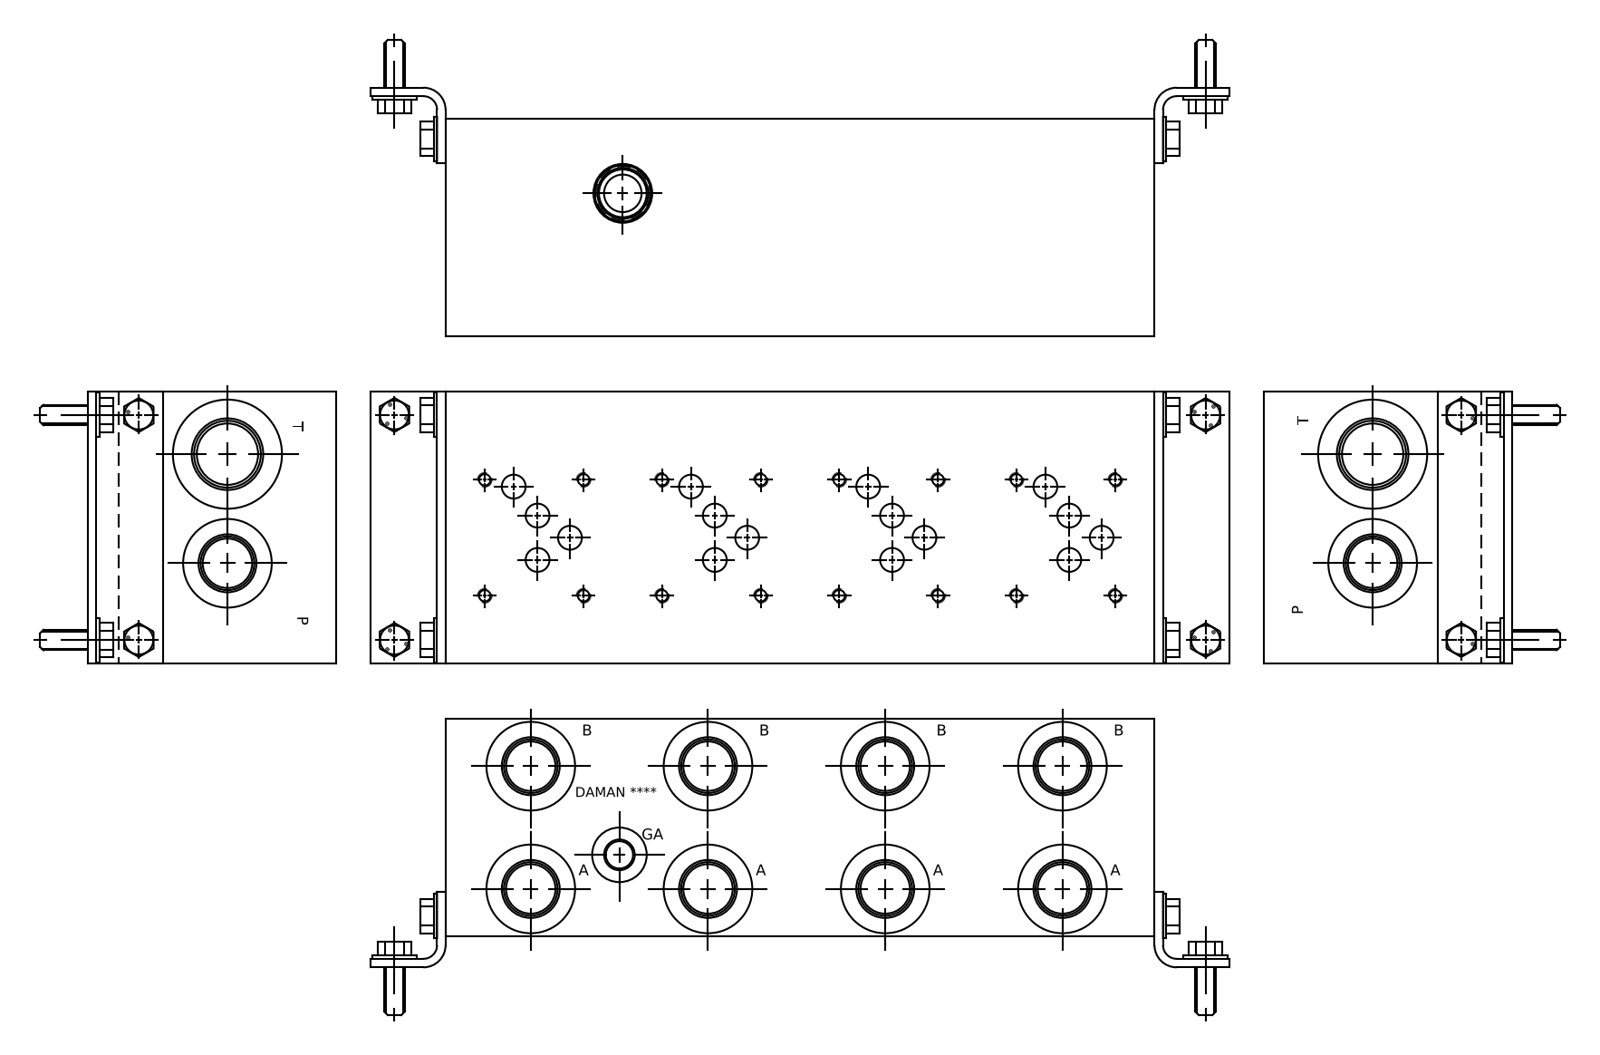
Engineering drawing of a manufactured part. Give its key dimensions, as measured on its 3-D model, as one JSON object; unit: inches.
{"part_name": "Part_DD05HP043S~S_3D", "step_written_by": "Autodesk Inventor 2019 (AUTOMOTIVE_DESIGN)", "units": "inches", "bodies": {"solids": 1, "faces": 876, "planar": 456, "cylindrical": 129, "other": 291}, "overall_size": [13, 5, 4], "volume_in3": 241.9, "surface_area_in2": 352.8, "round_holes": [[0.201, 16], [0.25, 16], [0.438, 14], [0.906, 9], [0.981, 9], [1.08, 9], [1.655, 9], [1.063, 8], [0.312, 2], [0.375, 2], [0.437, 2], [1.063, 2]], "face_to_face_distances": [4, 5, 13, 0.031, 4.969, 12.969, 12.938, 0.75, 0.781, 4.219], "hole_center_spacings": [3.25, 6.5, 3.883, 2.793, 0.719, 1.813, 2.687, 3.953]}
